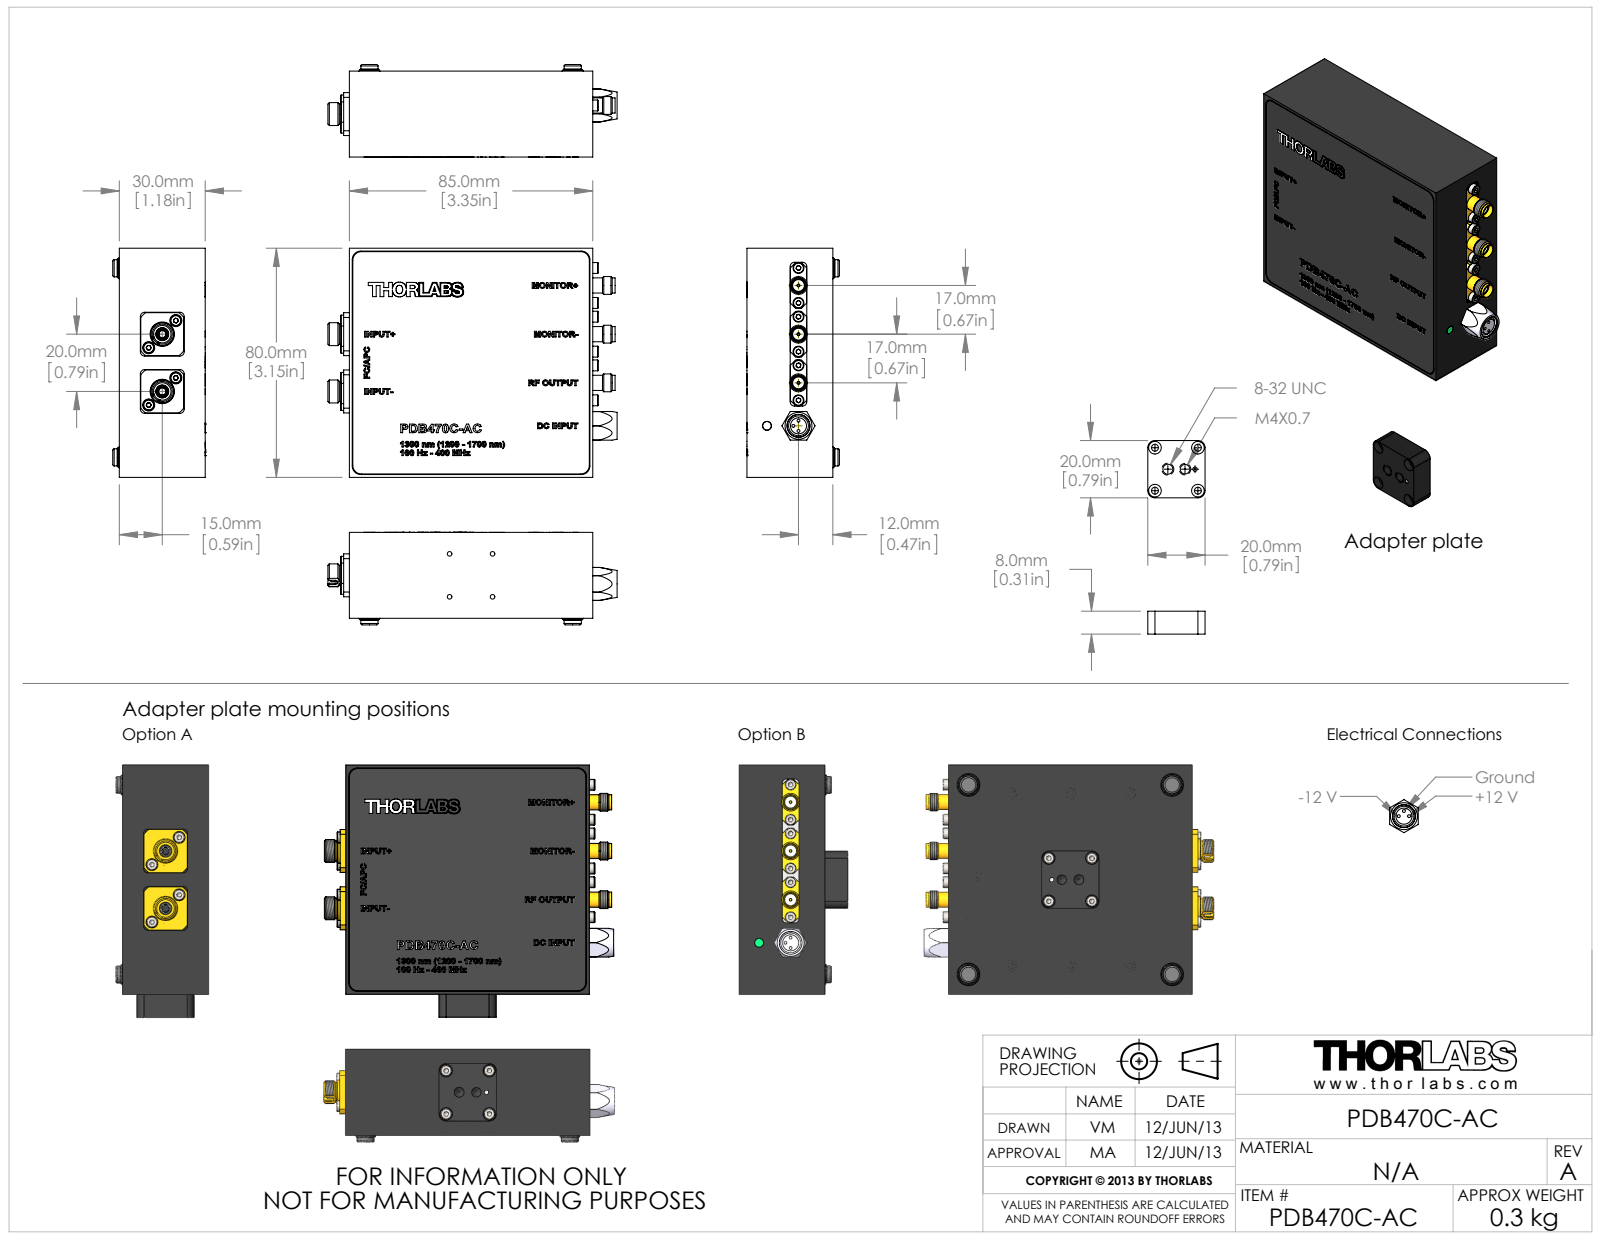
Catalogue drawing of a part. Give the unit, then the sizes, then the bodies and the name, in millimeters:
Units: millimetres
Overall size (bounding box): 101 × 88 × 38
Round holes (diameter × count): ⌀1.6 ×29, ⌀2.4 ×8, ⌀4.4 ×8, ⌀8 ×7, ⌀2.6 ×6, ⌀1.5 ×4, ⌀0.8 ×3, ⌀1 ×3, ⌀4.1 ×3, ⌀4.2 ×3, ⌀4.7 ×3, ⌀3.2 ×2
Round bosses / shafts (diameter × count): ⌀3.8 ×25, ⌀2 ×25, ⌀4.2 ×8, ⌀2.3 ×8, ⌀6 ×6, ⌀1.57 ×4, ⌀6.22 ×3, ⌀5.3 ×3
Partial cylindrical surfaces — rounded edges, fillets, slot ends (radius × count): R1.5 ×12, R3 ×12, R5 ×10, R2.5 ×8, R1.02 ×4, R8 ×3, R9.5 ×2, R5.75 ×1
Main face-to-face distances: 30, 29.7, 6, 23.7, 24, 5.5, 80, 85, 2, 74.5
Hole centre spacings: 15, 8.75, 12.9, 6.1, 17, 2.83, 7.57, 10.9
Volume: 89 116 mm³ · Surface area: 58 103 mm²
Bodies: 84 solids, 3162 faces (1813 planar, 542 cylindrical, 807 other)
Part name (STEP PRODUCT): M0075-22-0001 PDA10Bx (RKMF); M0092-0699 Grundkörper PDB480C-AC Rev C; PDB480C-AC Rev C; M0091-90-0003 PDA10Bx (Gerätefüsse) (+8 more)
STEP written by: SolidWorks 2012 (AUTOMOTIVE_DESIGN)
